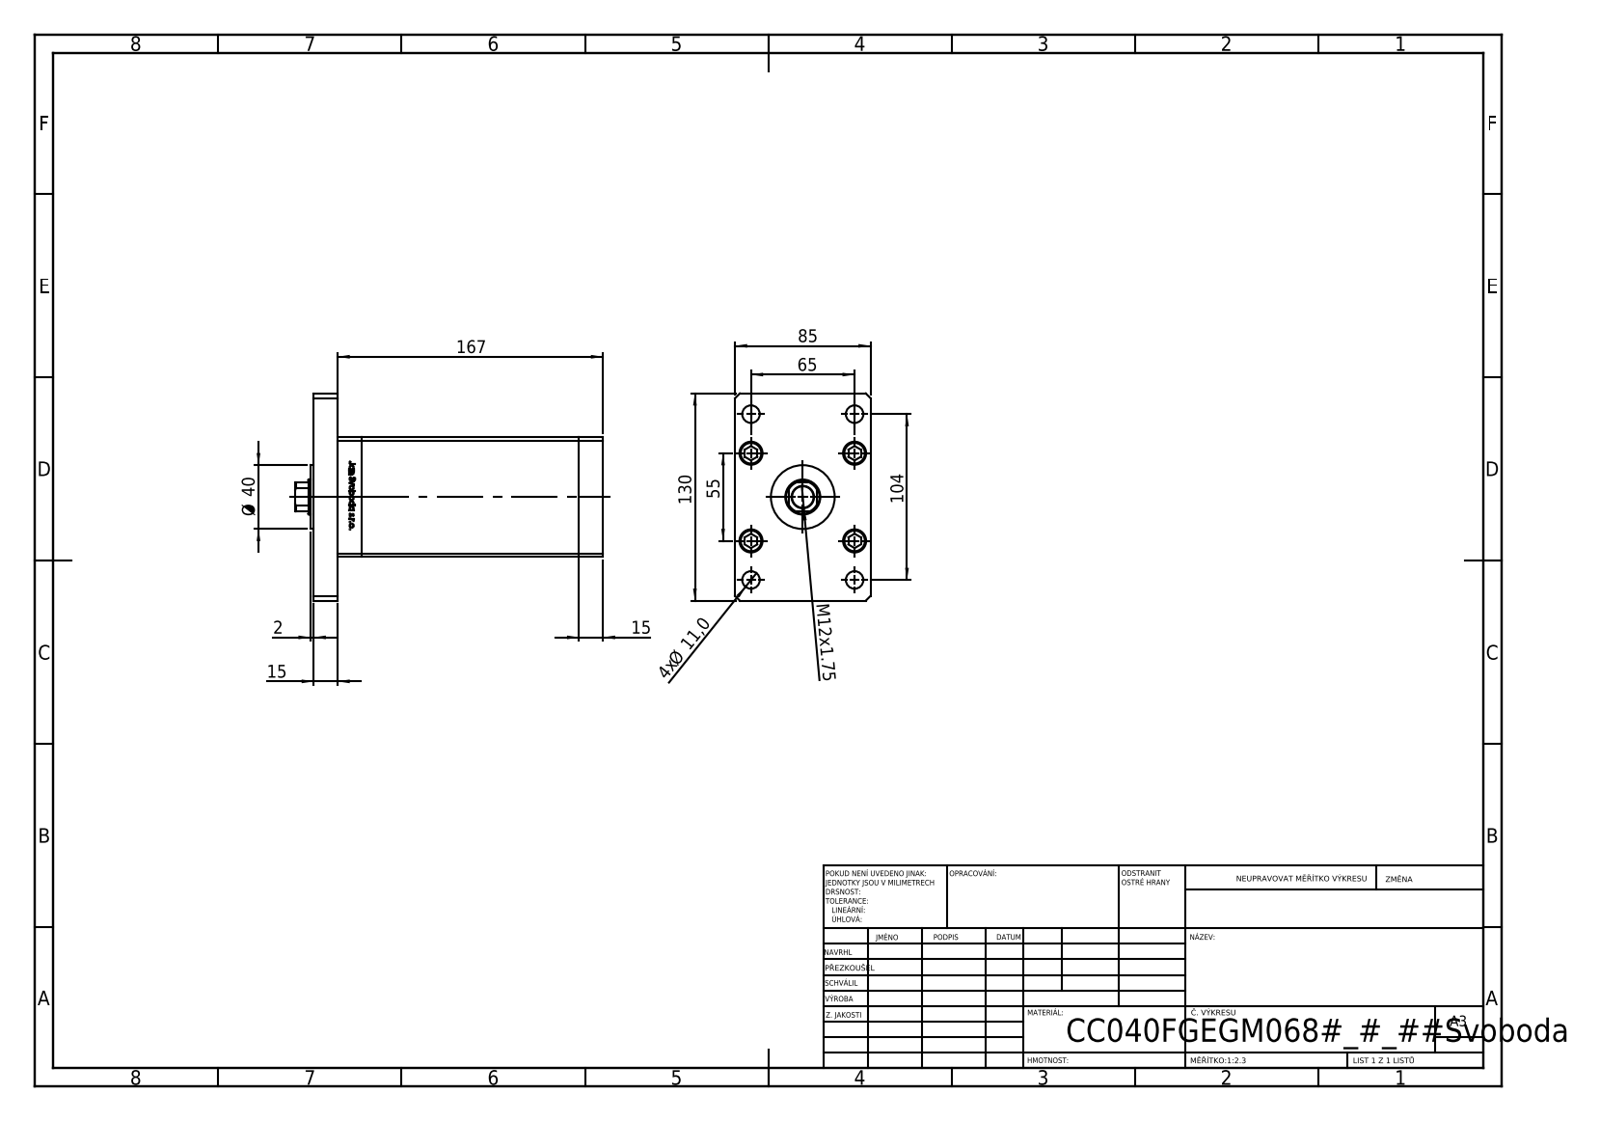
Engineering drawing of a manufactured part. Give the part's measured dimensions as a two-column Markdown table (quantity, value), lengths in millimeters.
| quantity | value |
| --- | --- |
| part name | V220C_F_MIDDLE; V220C_VC_F; V220C BACK_F; ALLEN BOLT (+2 more) |
| STEP written by | SolidWorks 2019 (CONFIG_CONTROL_DESIGN) |
| units | millimeters |
| bodies | 19 solids, 1310 faces (517 planar, 187 cylindrical, 606 other) |
| overall size | 193 × 130 × 85 |
| volume | 1 102 000 mm³ |
| surface area | 192 475 mm² |
| round holes (diameter × count) | 11 × 9, 15.5 × 5, 10 × 4, 14.5 × 4, 2 × 2, 13.16 × 2, 13.5 × 1, 22 × 1, 23.5 × 1 |
| round bosses / shafts (diameter × count) | 8 × 9, 14.5 × 5, 40 × 1 |
| partial cylindrical surfaces (radius × count) | 0.93 × 2, 10.5 × 1 |
| main face-to-face distances | 15, 151.5, 166.5, 85, 75, 30, 136.5, 181.5, 10.5, 27.5 |
| hole center spacings | 28, 24.5, 42.57, 61.32, 65, 69.46, 79.5, 102.69 |
